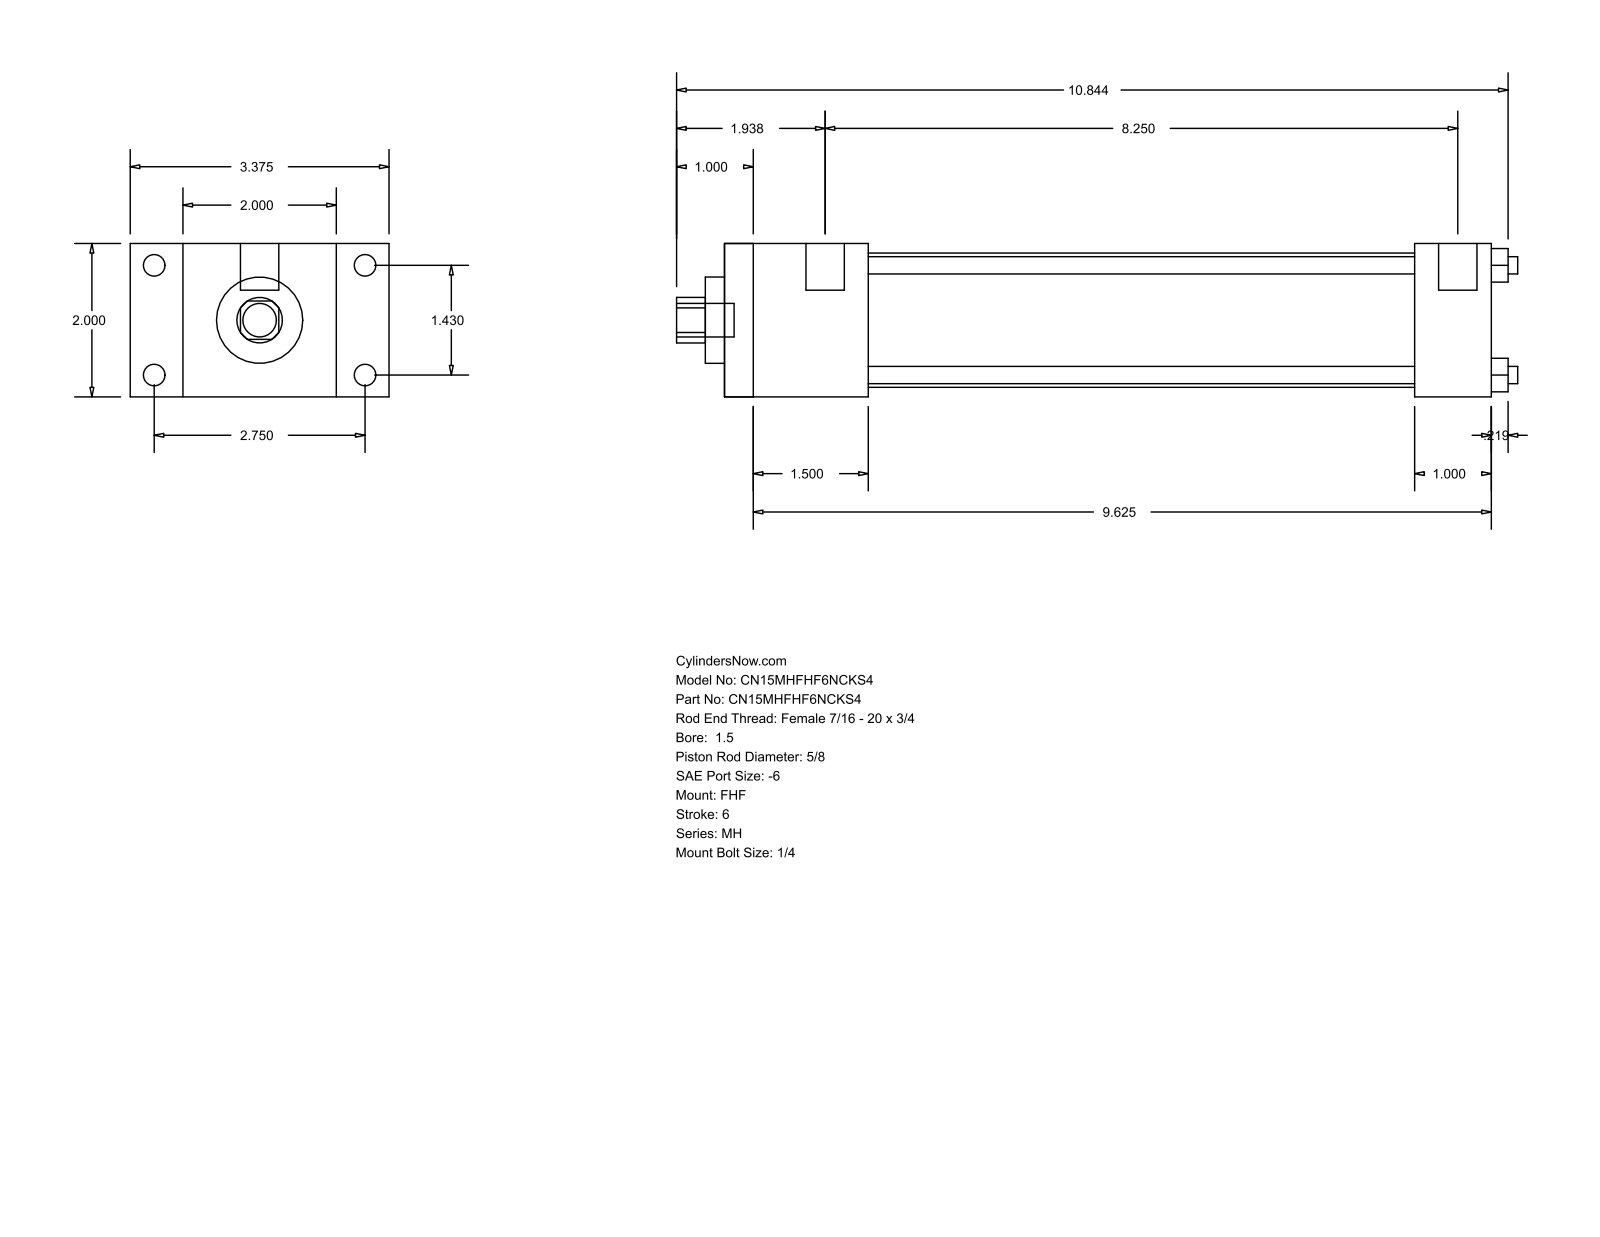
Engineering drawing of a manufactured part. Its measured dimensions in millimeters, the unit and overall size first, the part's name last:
Units: millimetres
Overall size (bounding box): 278.61 × 85.72 × 50.8
Round holes (diameter × count): ⌀5.71 ×4, ⌀15.88 ×1, ⌀28.57 ×1, ⌀44.45 ×1
Round bosses / shafts (diameter × count): ⌀7.14 ×4, ⌀5.56 ×4, ⌀12.7 ×2, ⌀11.11 ×1
Partial cylindrical surfaces — rounded edges, fillets, slot ends (radius × count): R7.54 ×1
Main face-to-face distances: 50.8, 17.46, 68.26, 47.62, 85.72, 254, 206.38, 228.59, 180.97, 25.41
Hole centre spacings: 25.68, 36.32, 51.36
Bodies: 0 solids, 88 faces (60 planar, 28 cylindrical, 0 other)
Part name (STEP PRODUCT): MH_FHF__0150_0.625
STEP written by: GSSL Pune (CONFIG_CONTROL_DESIGN)
